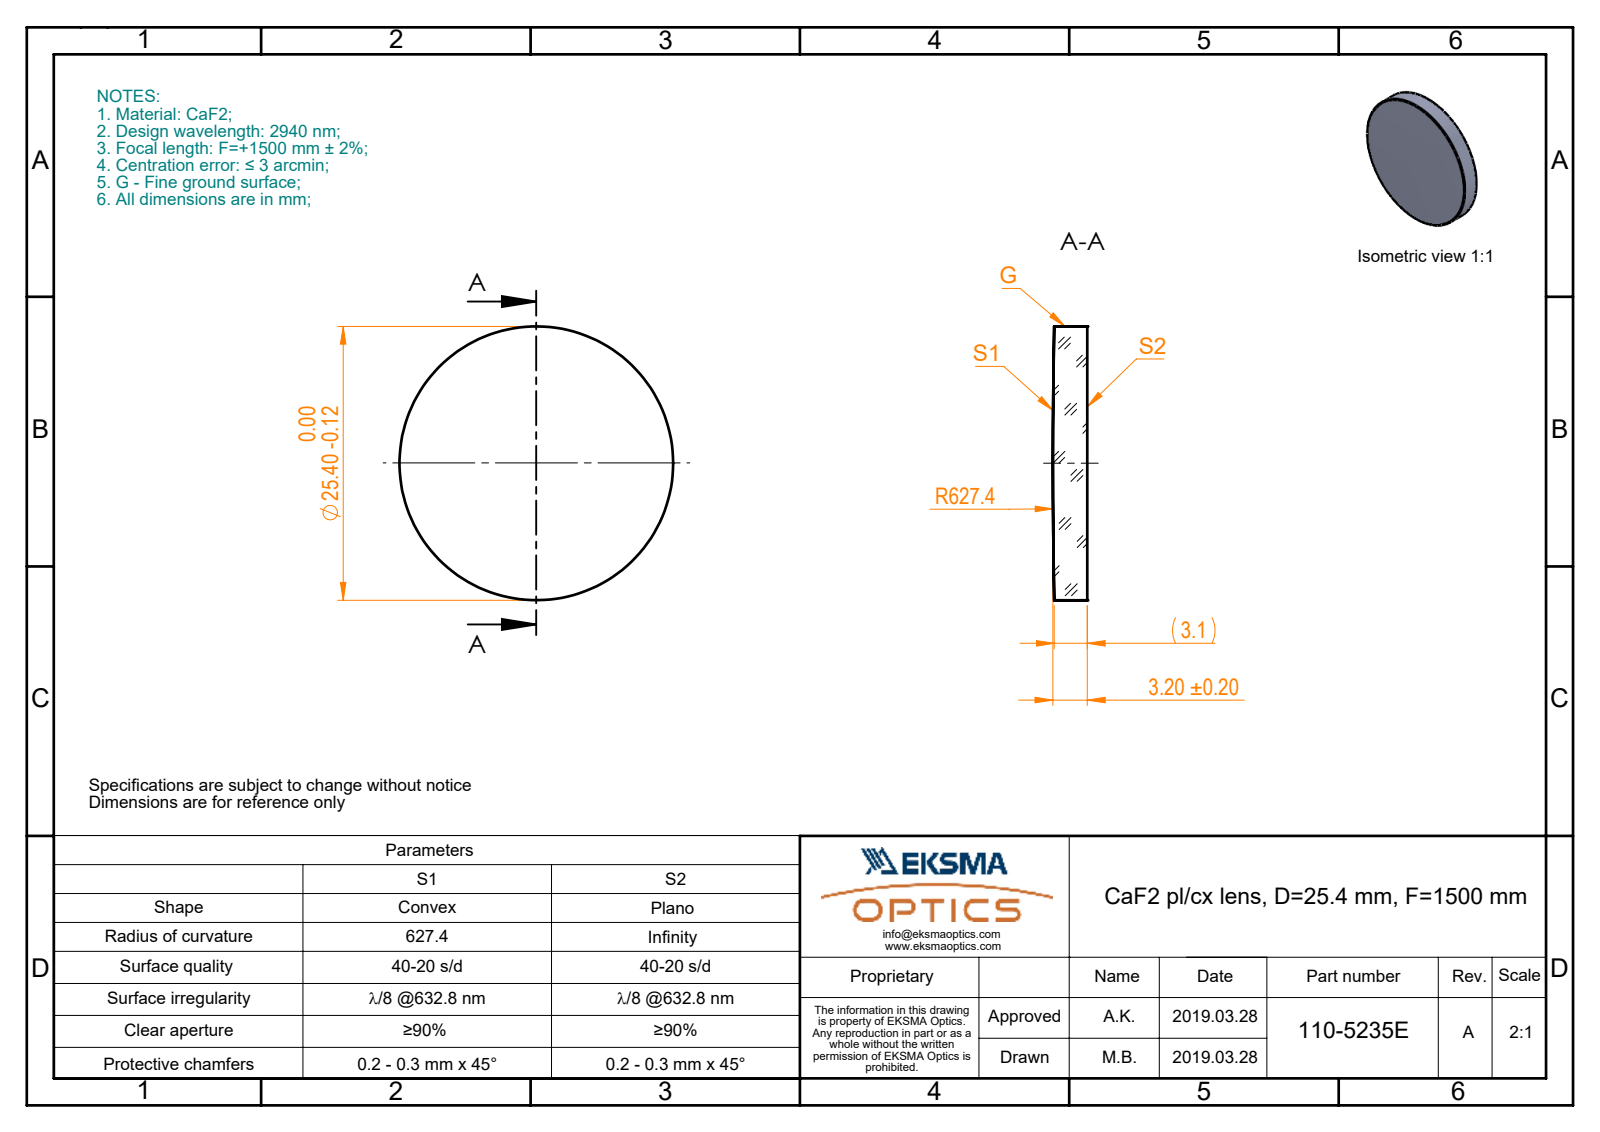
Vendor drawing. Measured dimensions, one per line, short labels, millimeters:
name: 110-5235E CaF2 pl-cx 25.4 F1500
written by: SolidWorks 2017 (CONFIG_CONTROL_DESIGN)
unit: mm
bodies: 1 solid, 5 faces (1 planar, 2 cylindrical, 2 other)
size: 25.4 × 25.4 × 3.2
volume: 1 589 mm³; area: 1 259 mm²
bosses: 1× ⌀25.4
